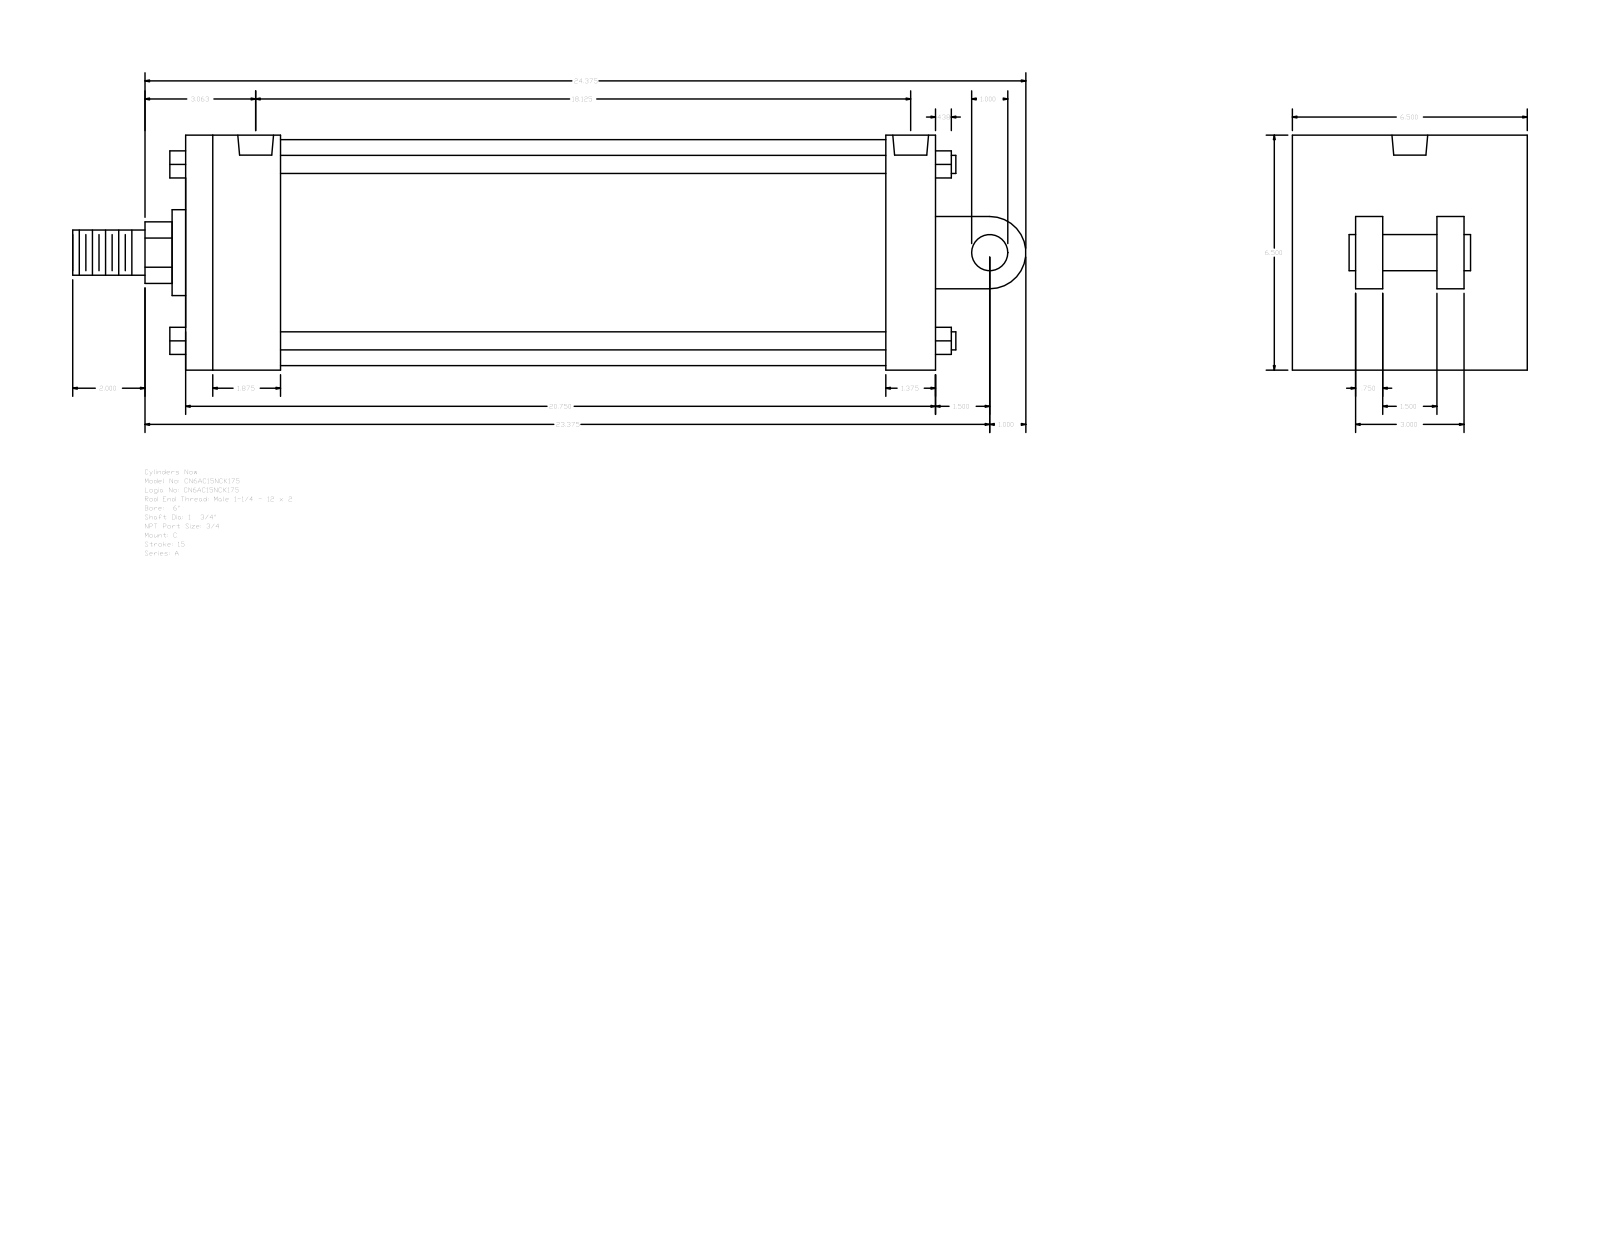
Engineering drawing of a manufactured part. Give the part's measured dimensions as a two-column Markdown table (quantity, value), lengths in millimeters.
| quantity | value |
| --- | --- |
| part name | A_C__0600_1.75 |
| STEP written by | GSSL Pune (CONFIG_CONTROL_DESIGN) |
| units | millimeters |
| bodies | 0 solids, 135 faces (102 planar, 33 cylindrical, 0 other) |
| overall size | 669.92 × 165.1 × 165.1 |
| round holes (diameter × count) | 15.08 × 4, 25.12 × 2 |
| round bosses / shafts (diameter × count) | 12.7 × 4, 158.75 × 1, 60.33 × 1, 44.45 × 1, 31.75 × 1, 25.4 × 1 |
| partial cylindrical surfaces (radius × count) | 21.63 × 1, 25.4 × 1 |
| main face-to-face distances | 165.1, 527.05, 19.05, 57.15, 66.68, 460.37, 492.13, 425.45, 34.92, 63.5 |
| hole center spacings | 5.56, 449.25, 454.81, 460.37 |
